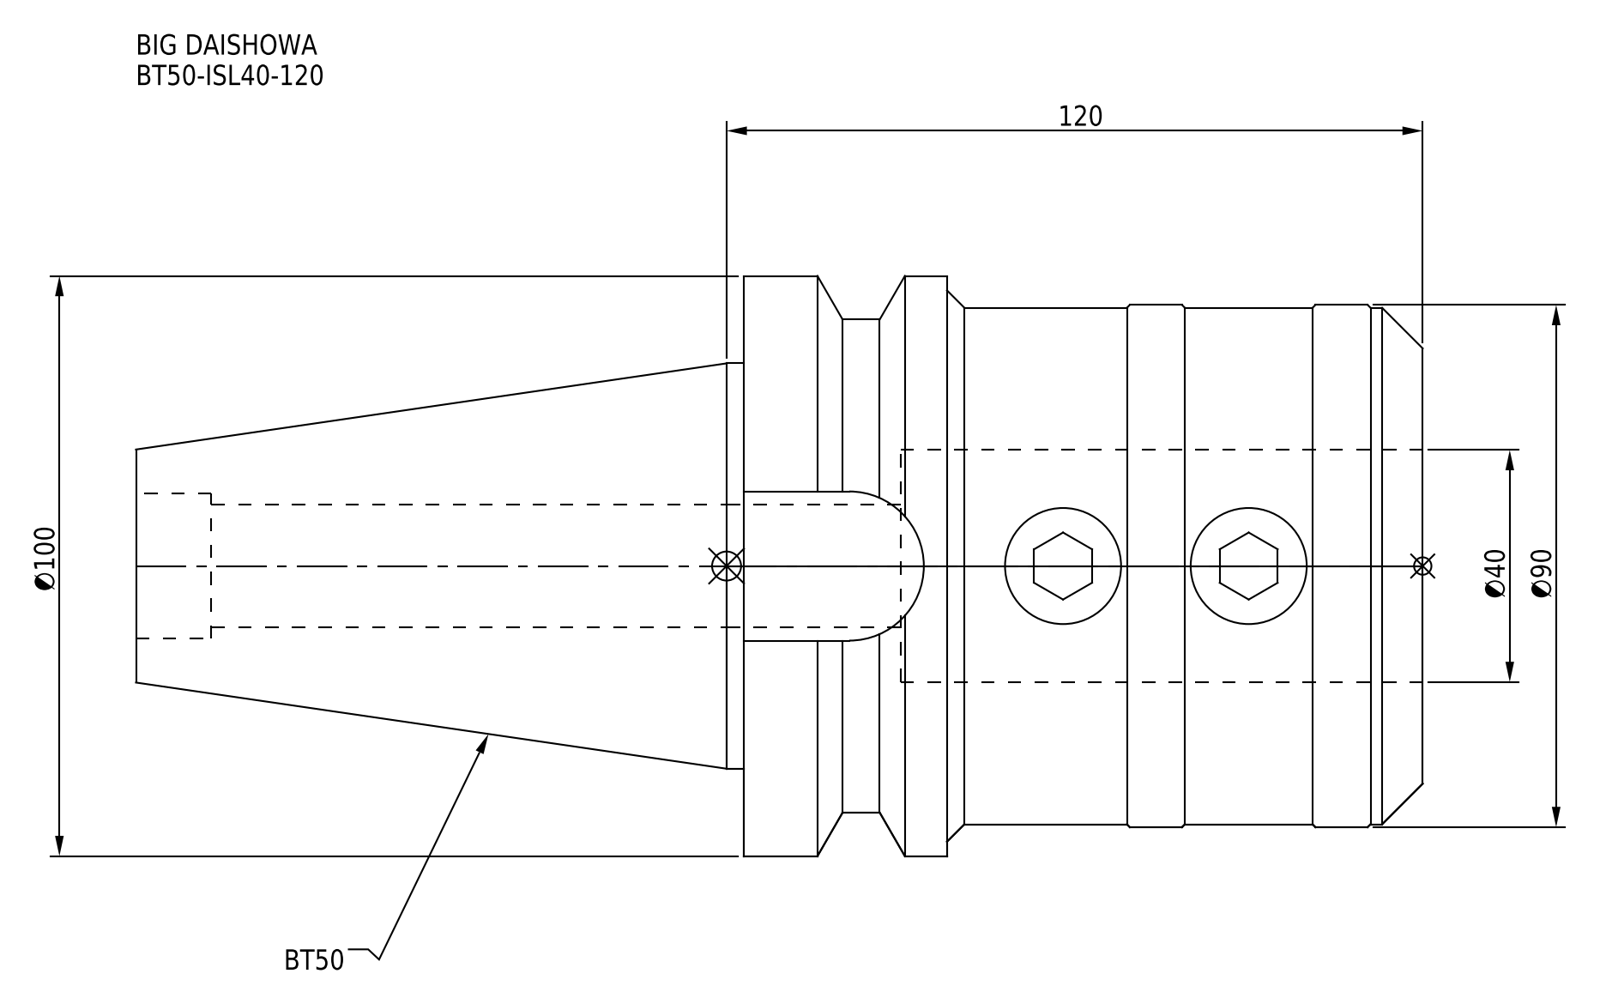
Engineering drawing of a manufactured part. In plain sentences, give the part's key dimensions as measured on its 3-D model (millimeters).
The part is named "BT50-ISL40-120". Its 3-D file was written by "CREO PARAMETRIC BY PTC INC, 2016380 (AUTOMOTIVE_DESIGN)". It is 1 solid with 58 faces: 12 planar, 28 cylindrical and 18 other. Overall it measures 221.8 by 100 by 100 millimeters. Its volume is 840 216 cubic millimeters and its surface area 86 203 square millimeters. Round holes: 1 of diameter 21.2, 1 of diameter 25, 1 of diameter 40. Round bosses or shafts: 1 of diameter 100, 1 of diameter 90, 1 of diameter 89, 1 of diameter 85, 1 of diameter 69.85. Partial cylindrical surfaces (rounded edges, fillets, slot ends): 1 of radius 12.85. The main face-to-face distances are 117, 90, 27, 221.8, 131.8, 104.8, 82, 8, 35, 139.8.
